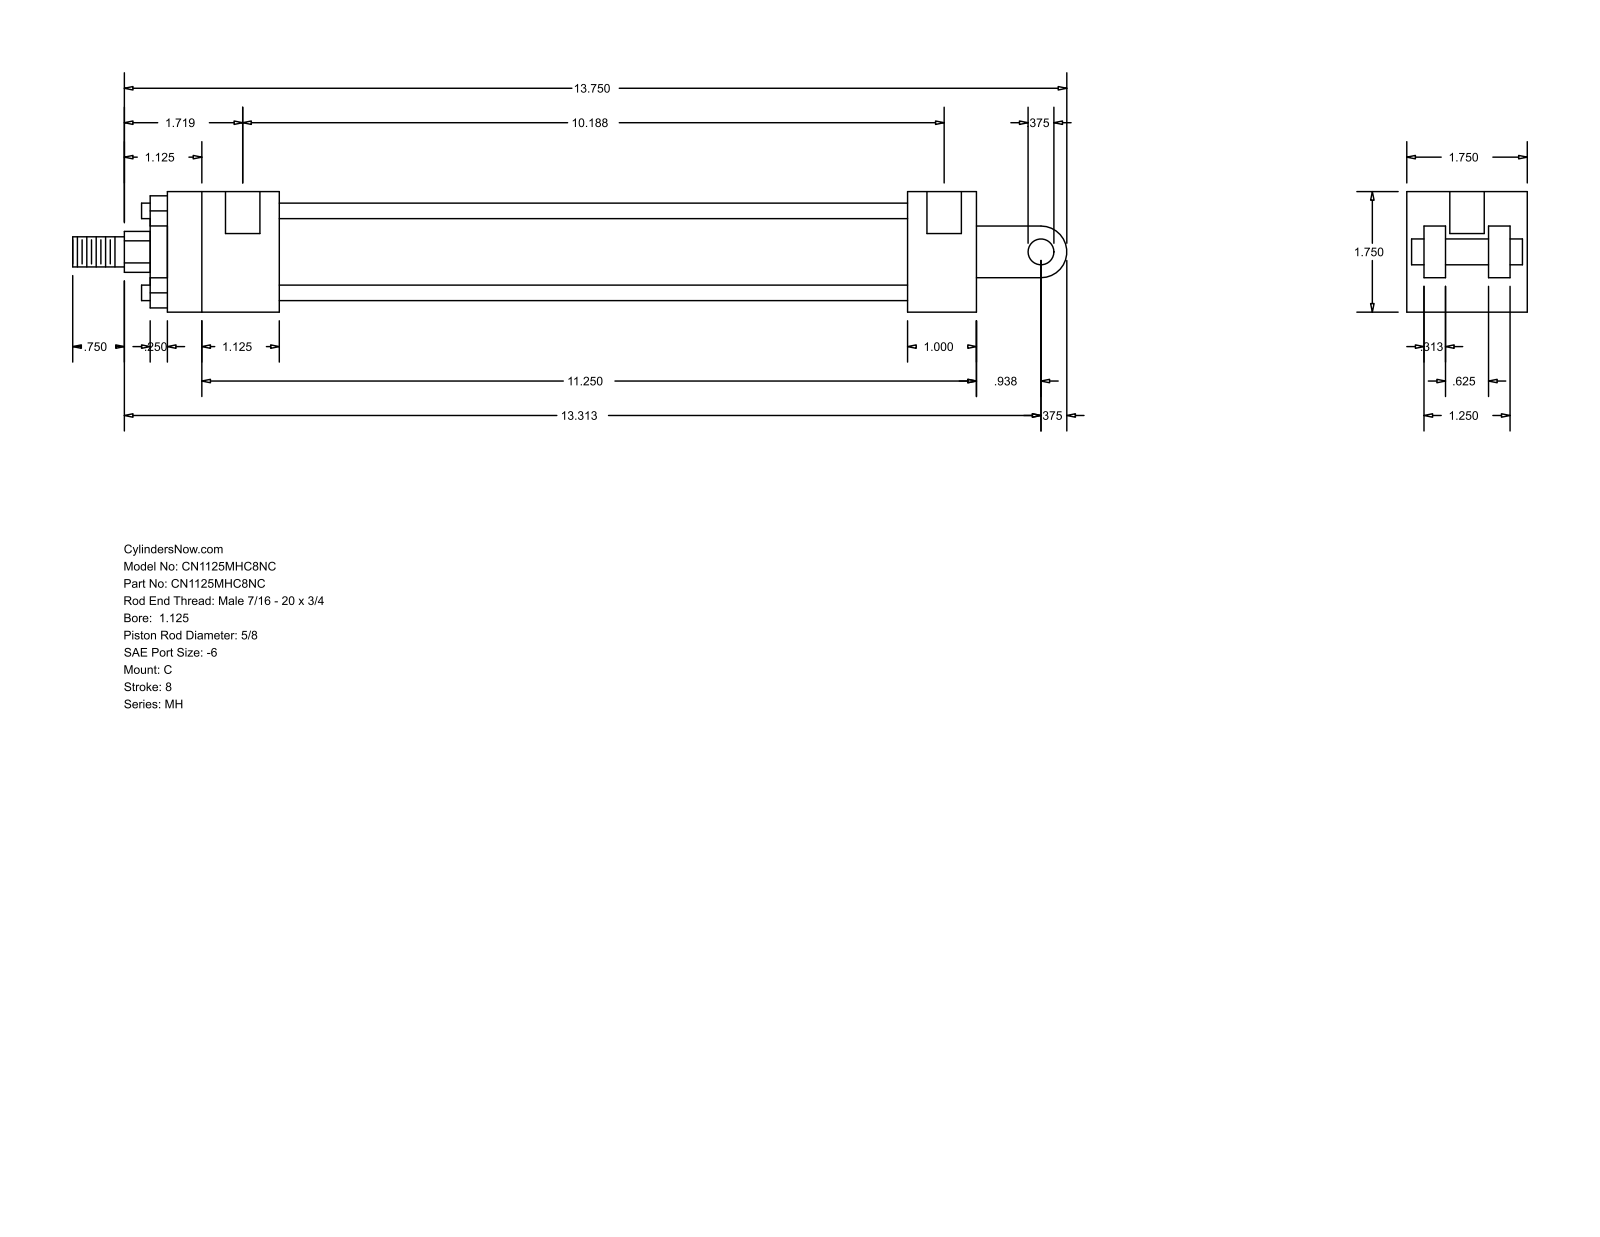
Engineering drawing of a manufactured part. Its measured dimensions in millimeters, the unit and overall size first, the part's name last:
Units: millimetres
Overall size (bounding box): 366.71 × 44.45 × 44.45
Round holes (diameter × count): ⌀5.56 ×4, ⌀12.7 ×2
Round bosses / shafts (diameter × count): ⌀5.71 ×4, ⌀34.92 ×1, ⌀28.57 ×1, ⌀15.88 ×1, ⌀11.11 ×1, ⌀9.53 ×1
Partial cylindrical surfaces — rounded edges, fillets, slot ends (radius × count): R7.54 ×1, R9.53 ×1
Main face-to-face distances: 44.46, 6.35, 31.76, 14.29, 30.17, 38.11, 7.94, 23.82, 41.27, 12.7
Hole centre spacings: 255.59, 3.17, 258.76
Bodies: 0 solids, 99 faces (70 planar, 29 cylindrical, 0 other)
Part name (STEP PRODUCT): MH_C__0112_0.625
STEP written by: GSSL Pune (CONFIG_CONTROL_DESIGN)
